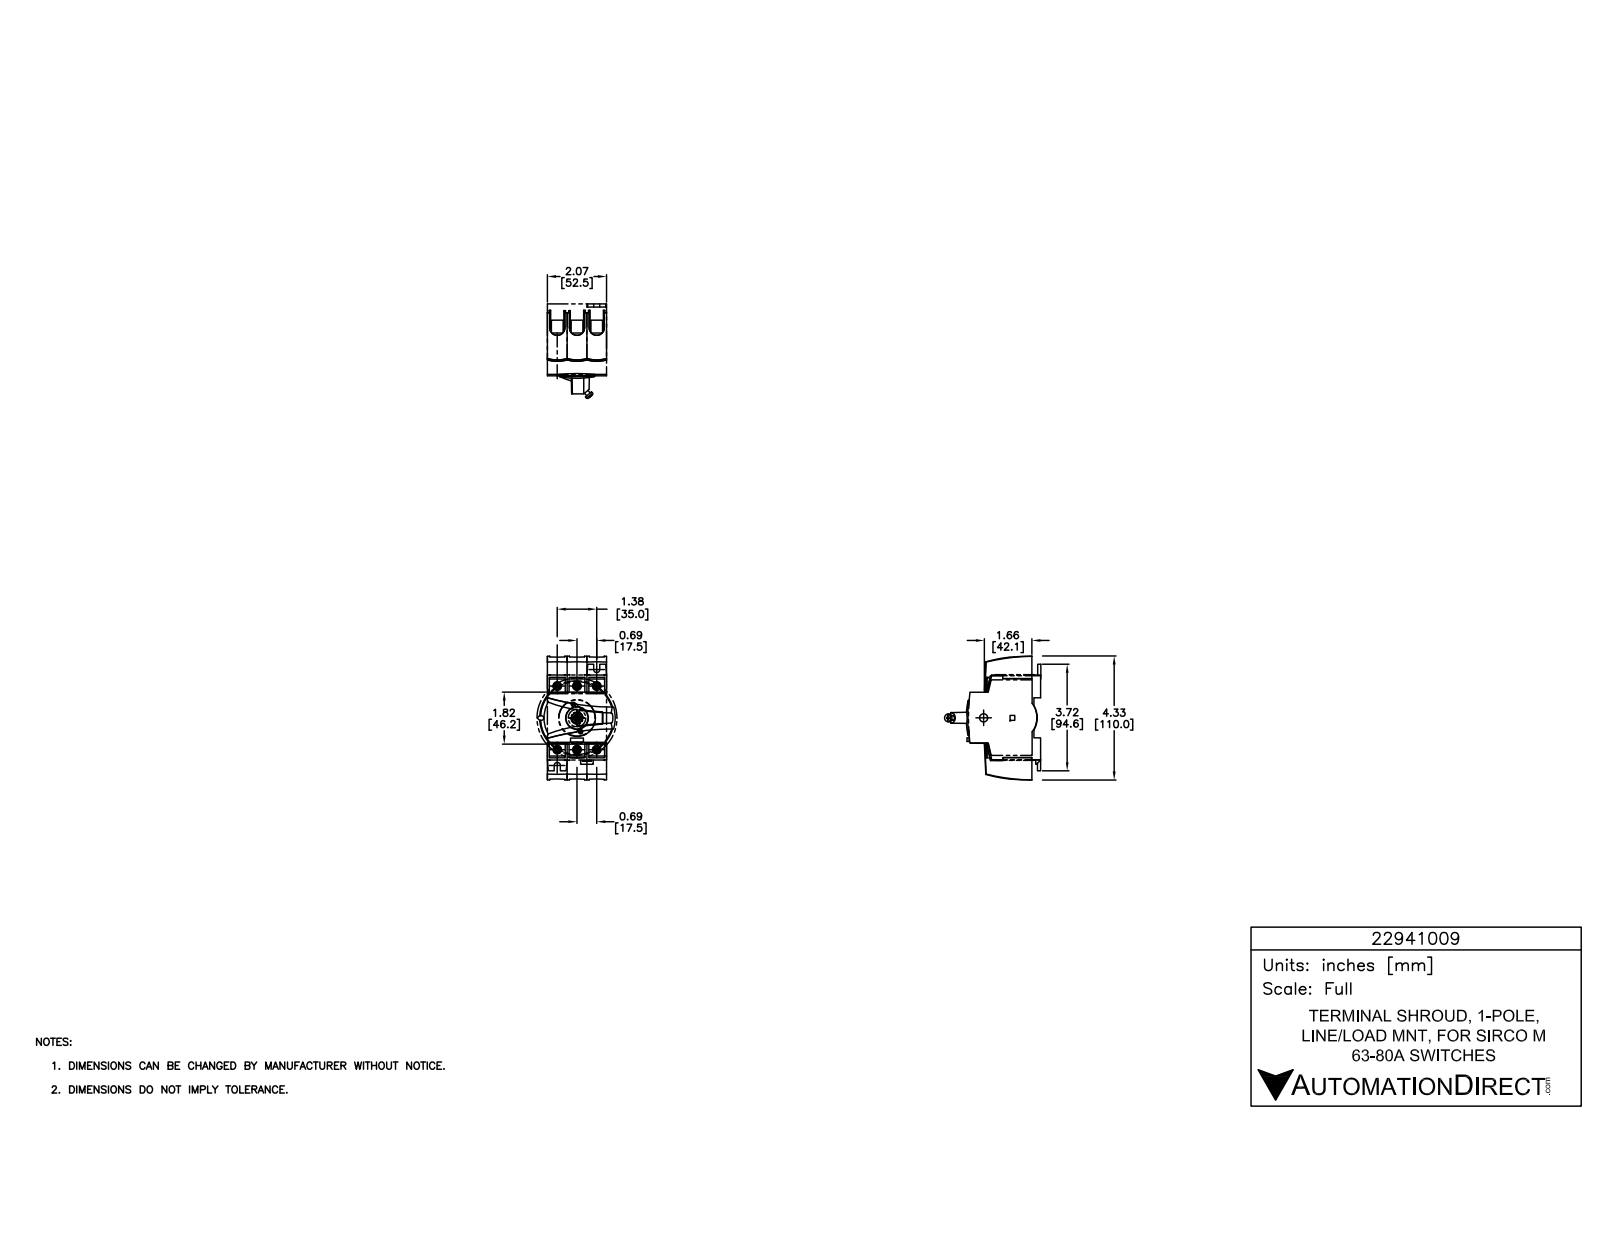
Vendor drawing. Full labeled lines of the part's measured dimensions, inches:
Part name (STEP PRODUCT): 22941009
STEP written by: SolidWorks 2015 (AUTOMOTIVE_DESIGN)
Units: inches
Bodies: 1 solid, 31 faces (17 planar, 4 cylindrical, 10 other)
Overall size (bounding box): 1.693 × 1.256 × 0.689
Volume: 0.17 in³ · Surface area: 7.478 in²
Partial cylindrical surfaces — rounded edges, fillets, slot ends (radius × count): R0.039 ×2, R0.264 ×1, R0.362 ×1
Main face-to-face distances: 0.047, 0.642, 0.689, 0.594, 0.081, 0.608, 0.033, 0.561, 0.528, 0.102
